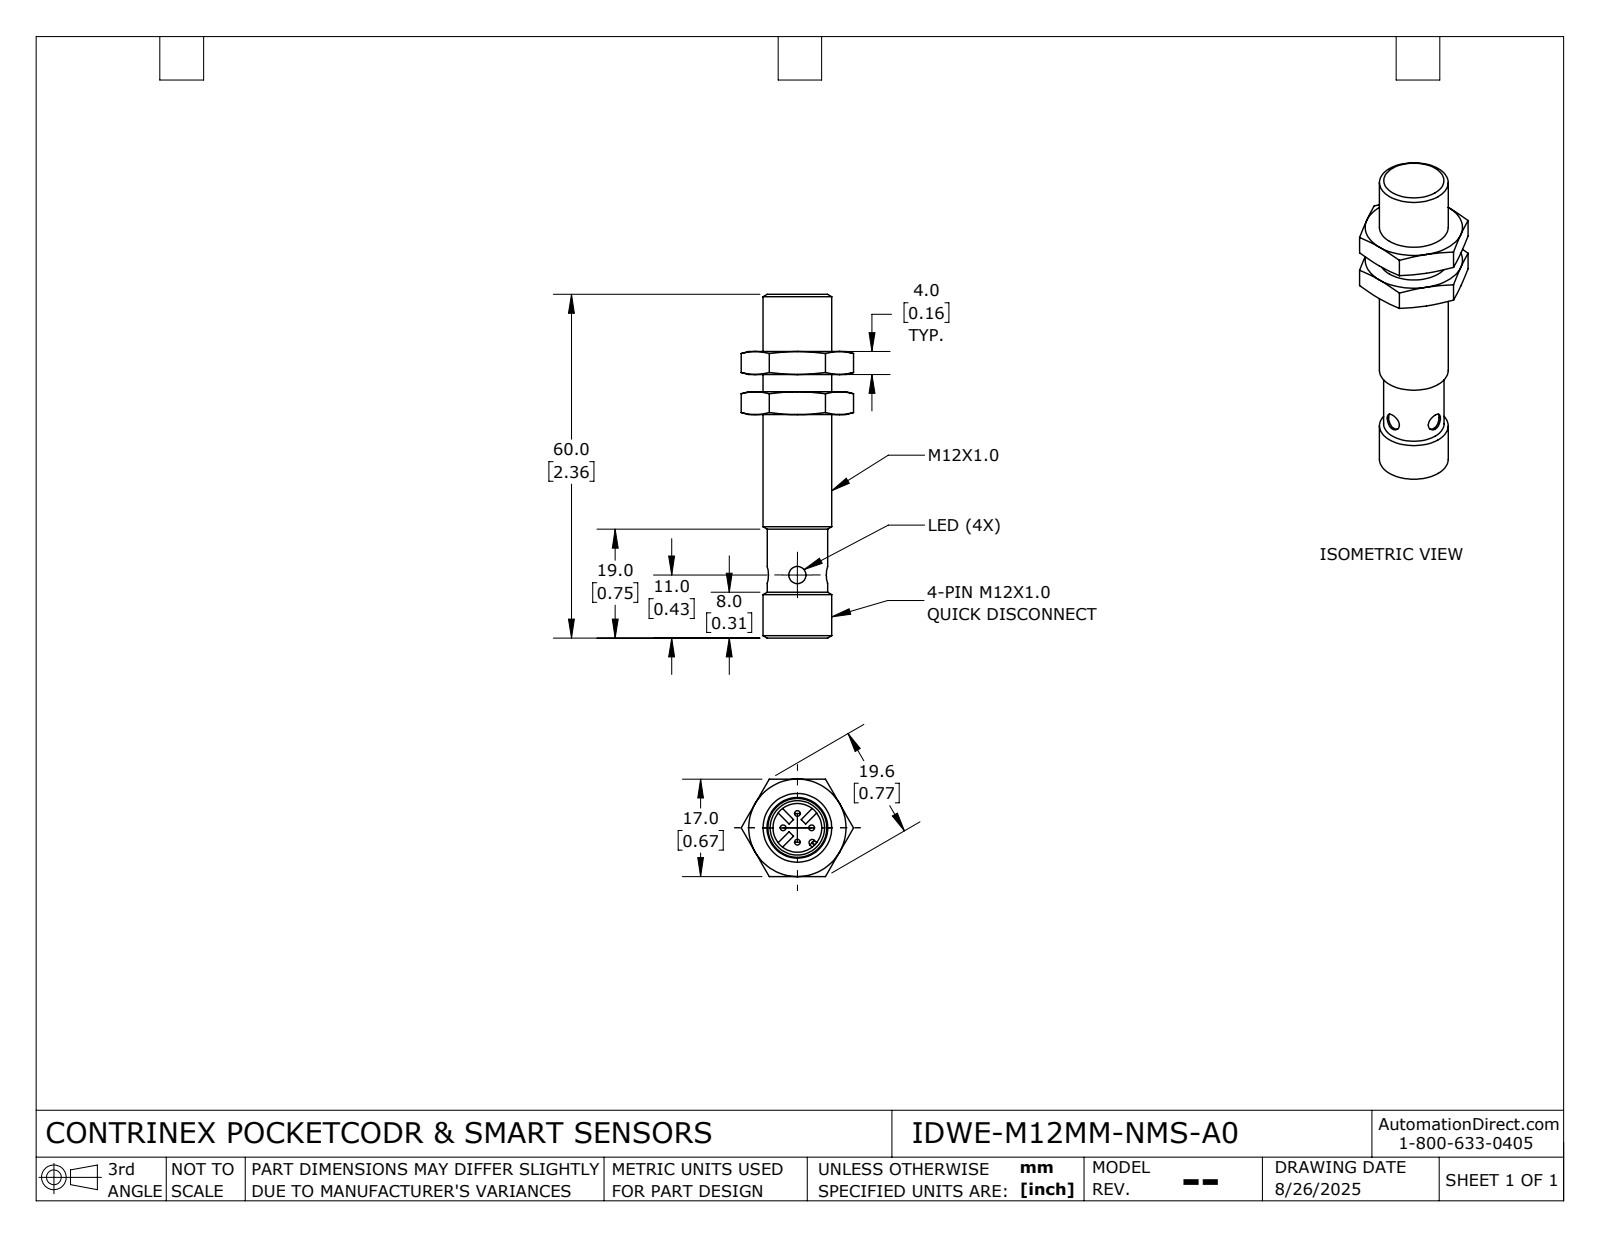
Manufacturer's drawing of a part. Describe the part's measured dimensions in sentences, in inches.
The part is named "IDWE-M12MM-NMS-A0". Its 3-D file was written by "SolidWorks 2024 (AUTOMOTIVE_DESIGN)". It is 3 solids with 115 faces: 35 planar, 29 cylindrical and 51 other. Overall it measures 2.362 by 0.773 by 0.669 inches. Its volume is 0.44 cubic inches and its surface area 6.374 square inches. Round holes: 2 of diameter 0.118, 1 of diameter 0.335, 1 of diameter 0.43. Round bosses or shafts: 4 of diameter 0.039, 1 of diameter 0.472, 1 of diameter 0.415. Partial cylindrical surfaces (rounded edges, fillets, slot ends): 2 of radius 0.02, 1 of radius 0.022. The main face-to-face distances are 0.669, 0.157, 0.276, 0.118, 0.433, 0.394, 0.551, 0.827, 2.02, 1.626.
